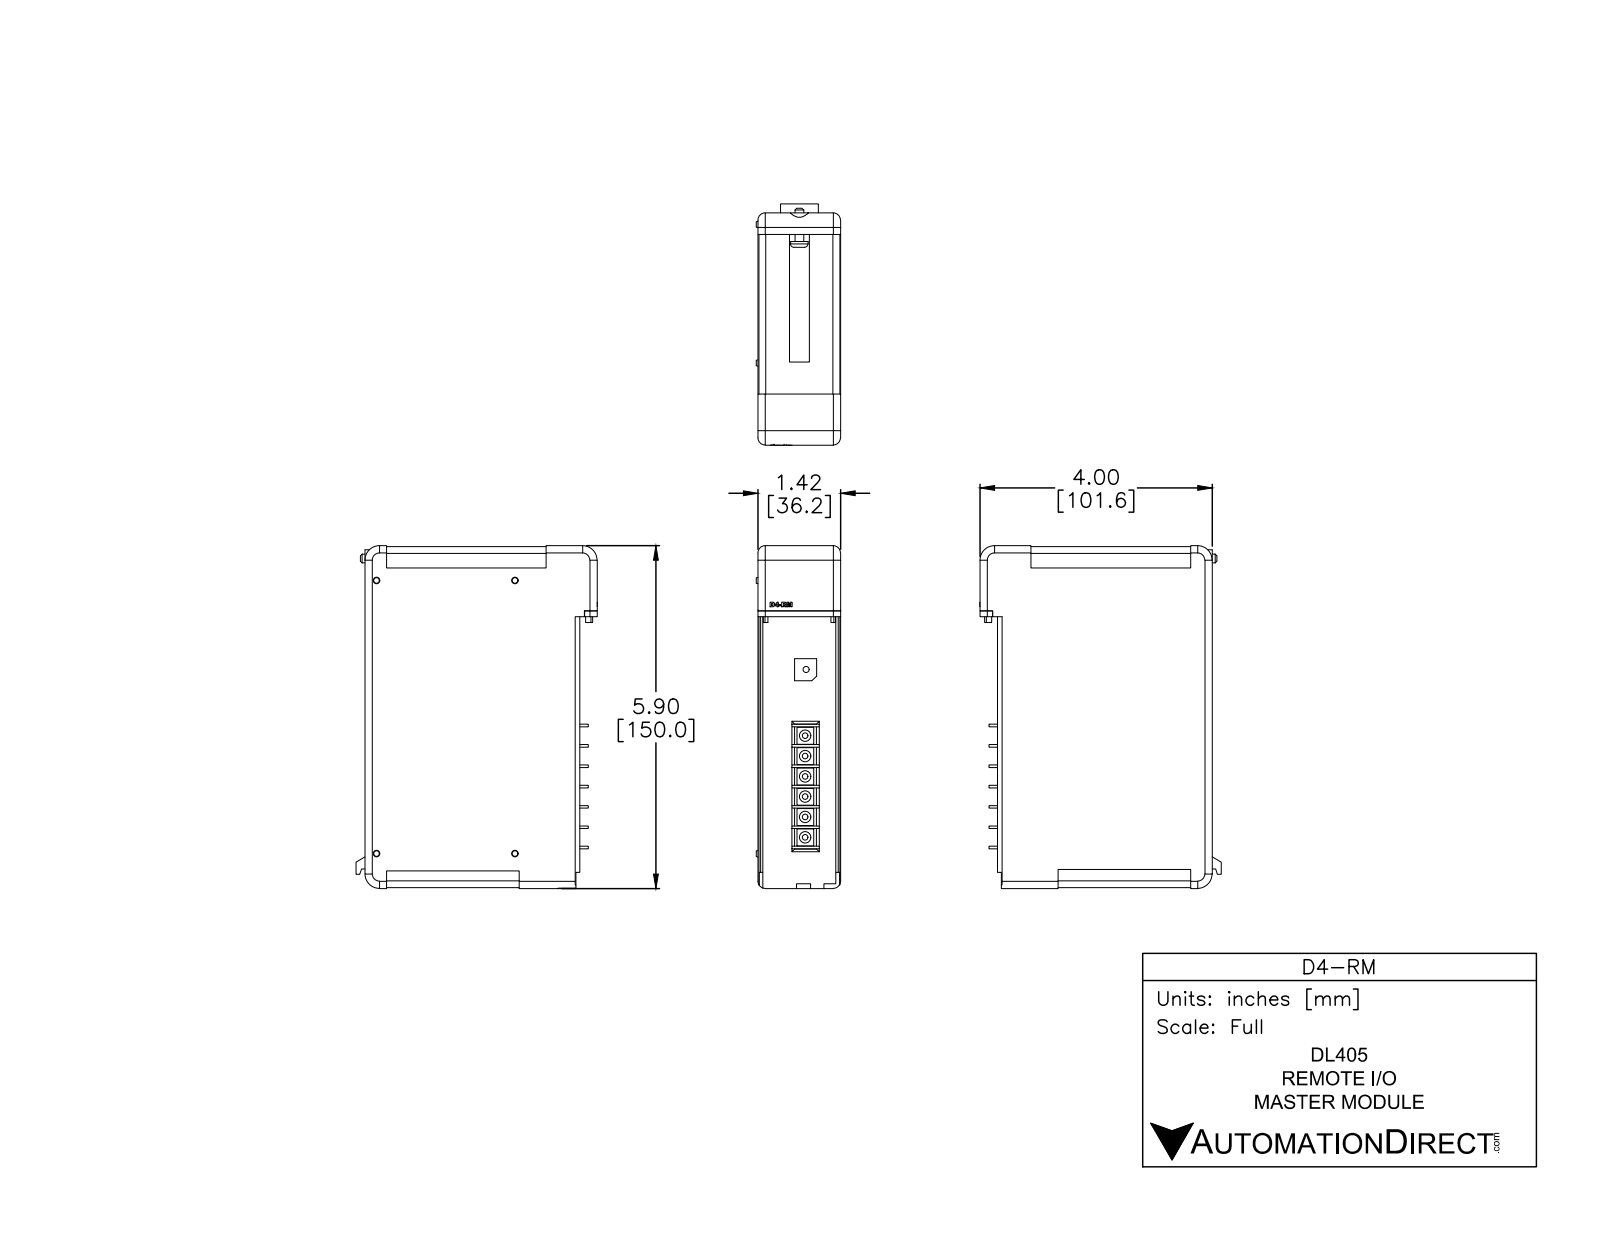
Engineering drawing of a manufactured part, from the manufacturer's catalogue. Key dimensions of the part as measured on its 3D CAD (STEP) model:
Part name (STEP PRODUCT): D4-RM
STEP written by: SolidWorks 2014 (AUTOMOTIVE_DESIGN)
Units: inches
Bodies: 8 solids, 365 faces (265 planar, 49 cylindrical, 51 other)
Overall size (bounding box): 5.905 × 4.156 × 1.455
Volume: 28.82 in³ · Surface area: 84.12 in²
Round holes (diameter × count): ⌀0.104 ×1
Round bosses / shafts (diameter × count): ⌀0.2 ×6, ⌀0.3 ×1, ⌀0.15 ×1
Partial cylindrical surfaces — rounded edges, fillets, slot ends (radius × count): R0.125 ×8, R0.12 ×4, R0.25 ×3, R0.015 ×2, R0.03 ×2, R0.151 ×1, R0.171 ×1
Main face-to-face distances: 1.425, 0.015, 3.325, 0.085, 1.34, 5.875, 0.07, 1.41, 1.325, 3.125
